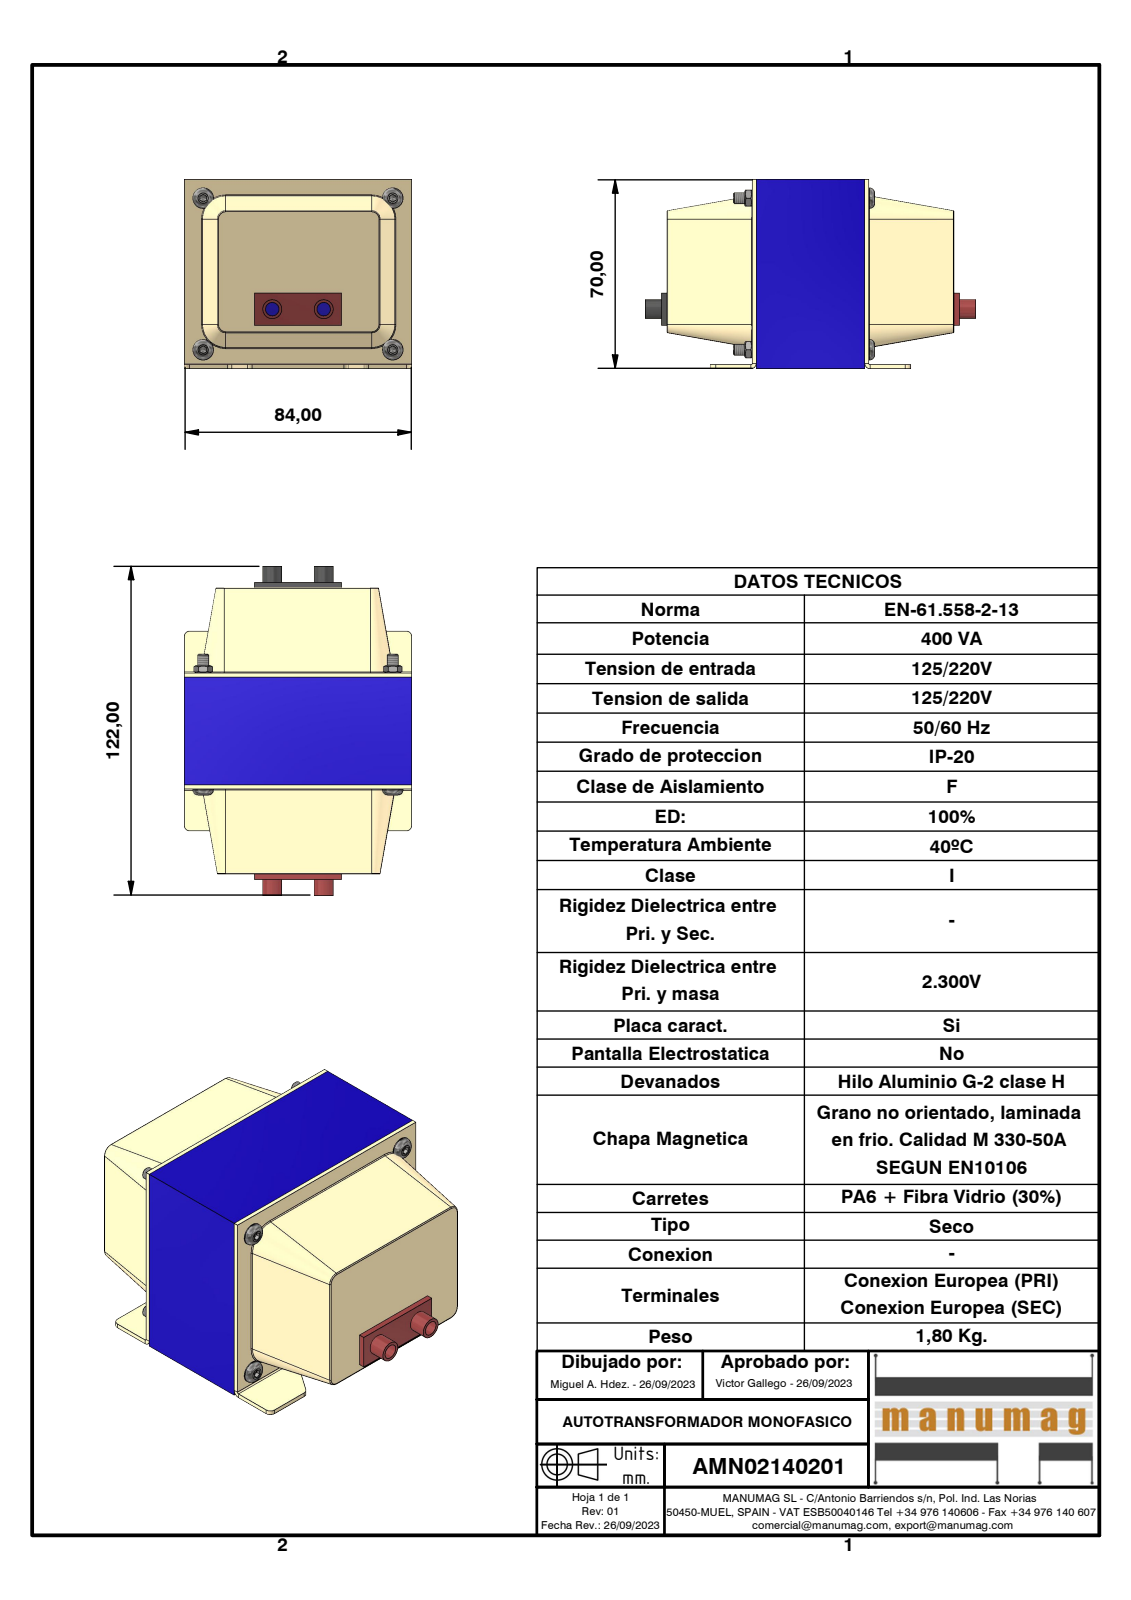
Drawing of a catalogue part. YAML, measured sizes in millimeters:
part_name: "AMN02140201; EI84 x 70 - 40 (RC28) Azul; TAPA RC28 RECEPTACULO; Receptaculo negro (+3 more)"
step_written_by: "Autodesk Inventor 2023 (AUTOMOTIVE_DESIGN)"
units: millimeters
bodies: {solids: 13, faces: 286, planar: 158, cylindrical: 64, other: 64}
overall_size: [122, 84, 70]
volume: 209325
surface_area: 89027
round_holes:
  - {diameter: 4, count: 8}
  - {diameter: 2.85, count: 4}
  - {diameter: 4.5, count: 4}
  - {diameter: 5, count: 2}
round_bosses_or_shafts:
  - {diameter: 7.6, count: 4}
  - {diameter: 7, count: 2}
partial_cylinders:
  - {radius: 0.38, count: 16}
  - {radius: 2, count: 14}
  - {radius: 0.5, count: 2}
face_to_face_distances: [1.5, 14, 73, 31.5, 56, 70, 62.51, 40, 28, 33]
hole_center_spacings: [70, 89.64, 46.96, 56, 29.58, 29.59, 48.27, 48.28]
